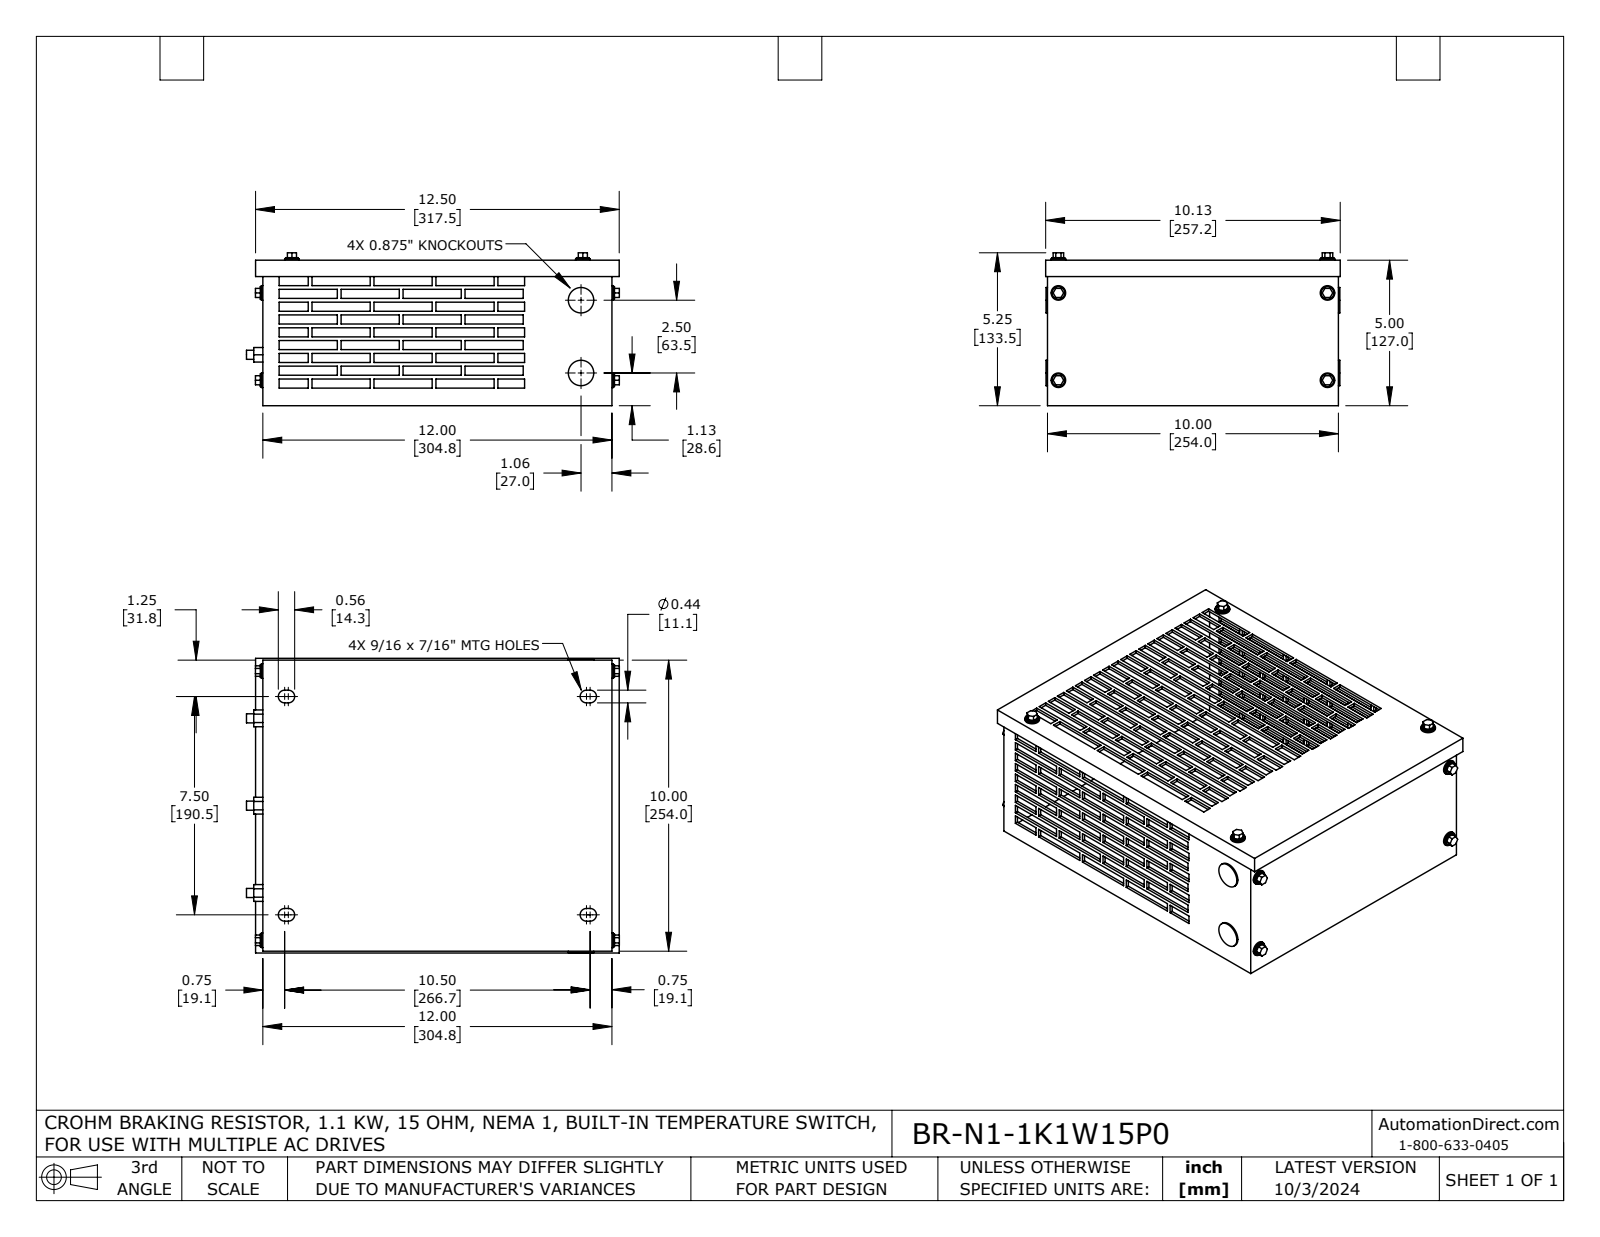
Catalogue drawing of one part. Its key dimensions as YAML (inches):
part_name: "BR-N1-1K2W15P0"
step_written_by: "SolidWorks 2021 (AUTOMOTIVE_DESIGN)"
units: inches
bodies: {solids: 32, faces: 981, planar: 879, cylindrical: 102, other: 0}
overall_size: [12.817, 10.125, 5.254]
volume: 37.32
surface_area: 826.2
round_holes:
  - {diameter: 0.25, count: 8}
  - {diameter: 0.75, count: 2}
round_bosses_or_shafts:
  - {diameter: 0.5, count: 8}
  - {diameter: 0.437, count: 8}
  - {diameter: 0.313, count: 3}
  - {diameter: 0.875, count: 2}
partial_cylinders:
  - {radius: 0.219, count: 8}
face_to_face_distances: [0.1, 4.9, 11.9, 5, 4.8, 9.9, 12, 11.8, 10, 9.8]
hole_center_spacings: [9.25, 3, 9.724, 10, 13.622, 2.5]
